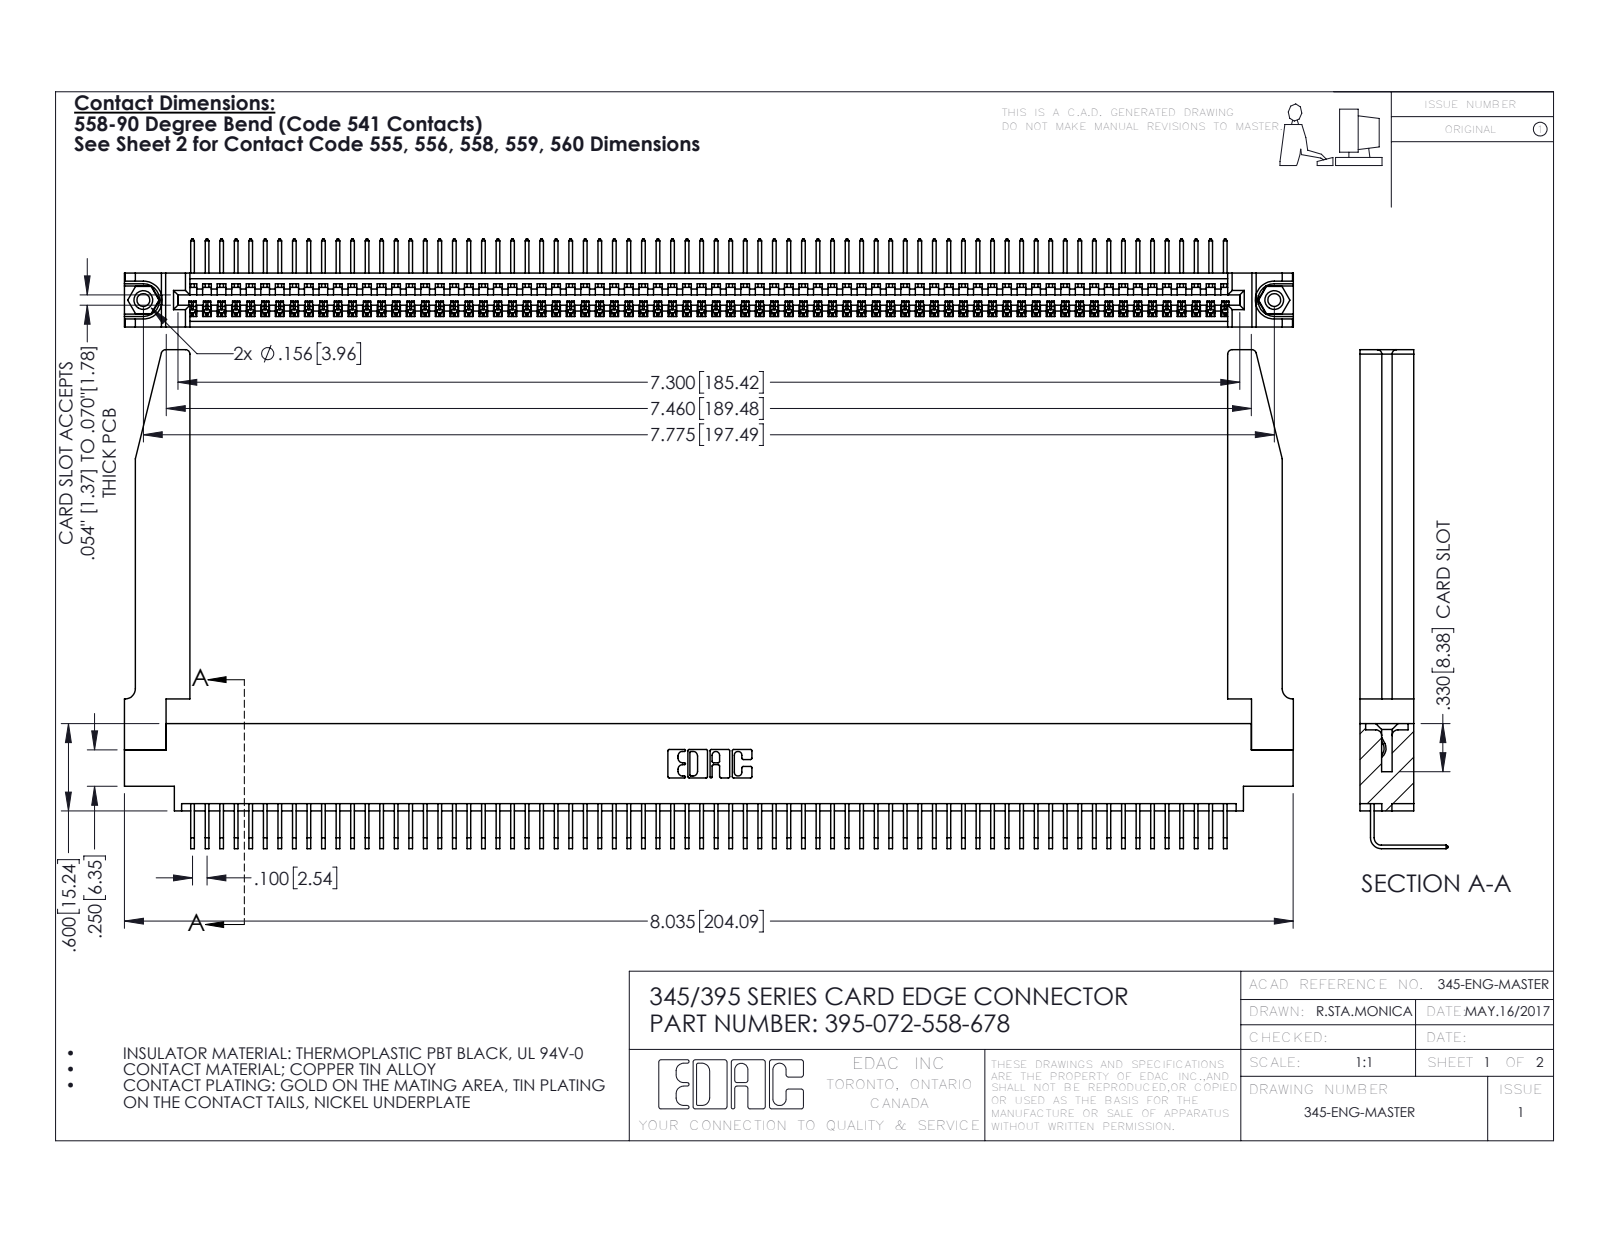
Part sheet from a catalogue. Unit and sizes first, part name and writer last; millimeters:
Units: millimetres
Overall size (bounding box): 204.1 × 87.1 × 15.4
Round holes (diameter × count): ⌀2.3 ×2, ⌀3.2 ×2, ⌀4 ×2, ⌀1.6 ×1
Round bosses / shafts (diameter × count): ⌀3.9 ×2
Partial cylindrical surfaces — rounded edges, fillets, slot ends (radius × count): R0.2 ×144, R0.3 ×22, R0.8 ×8, R0.2 ×6, R0.8 ×6, R0.7 ×3, R0.8 ×2, R1 ×2
Main face-to-face distances: 1.8, 9.4, 7.6, 2.5, 6.9, 0.6, 5.1, 5.7, 3.8, 4.4
Hole centre spacings: 6.9, 191.5, 197.5
Volume: 27 530 mm³ · Surface area: 35 050 mm²
Bodies: 77 solids, 4684 faces (3250 planar, 1382 cylindrical, 52 other)
Part name (STEP PRODUCT): 345 Part_0.170 Offset - 0.156 Dia-TH; 345-250-001_345-250-001-102; 345-220-078_345-220-078; 345-292-001_558 Tail - 2 (+1 more)
STEP written by: SolidWorks 2016 (CONFIG_CONTROL_DESIGN)
